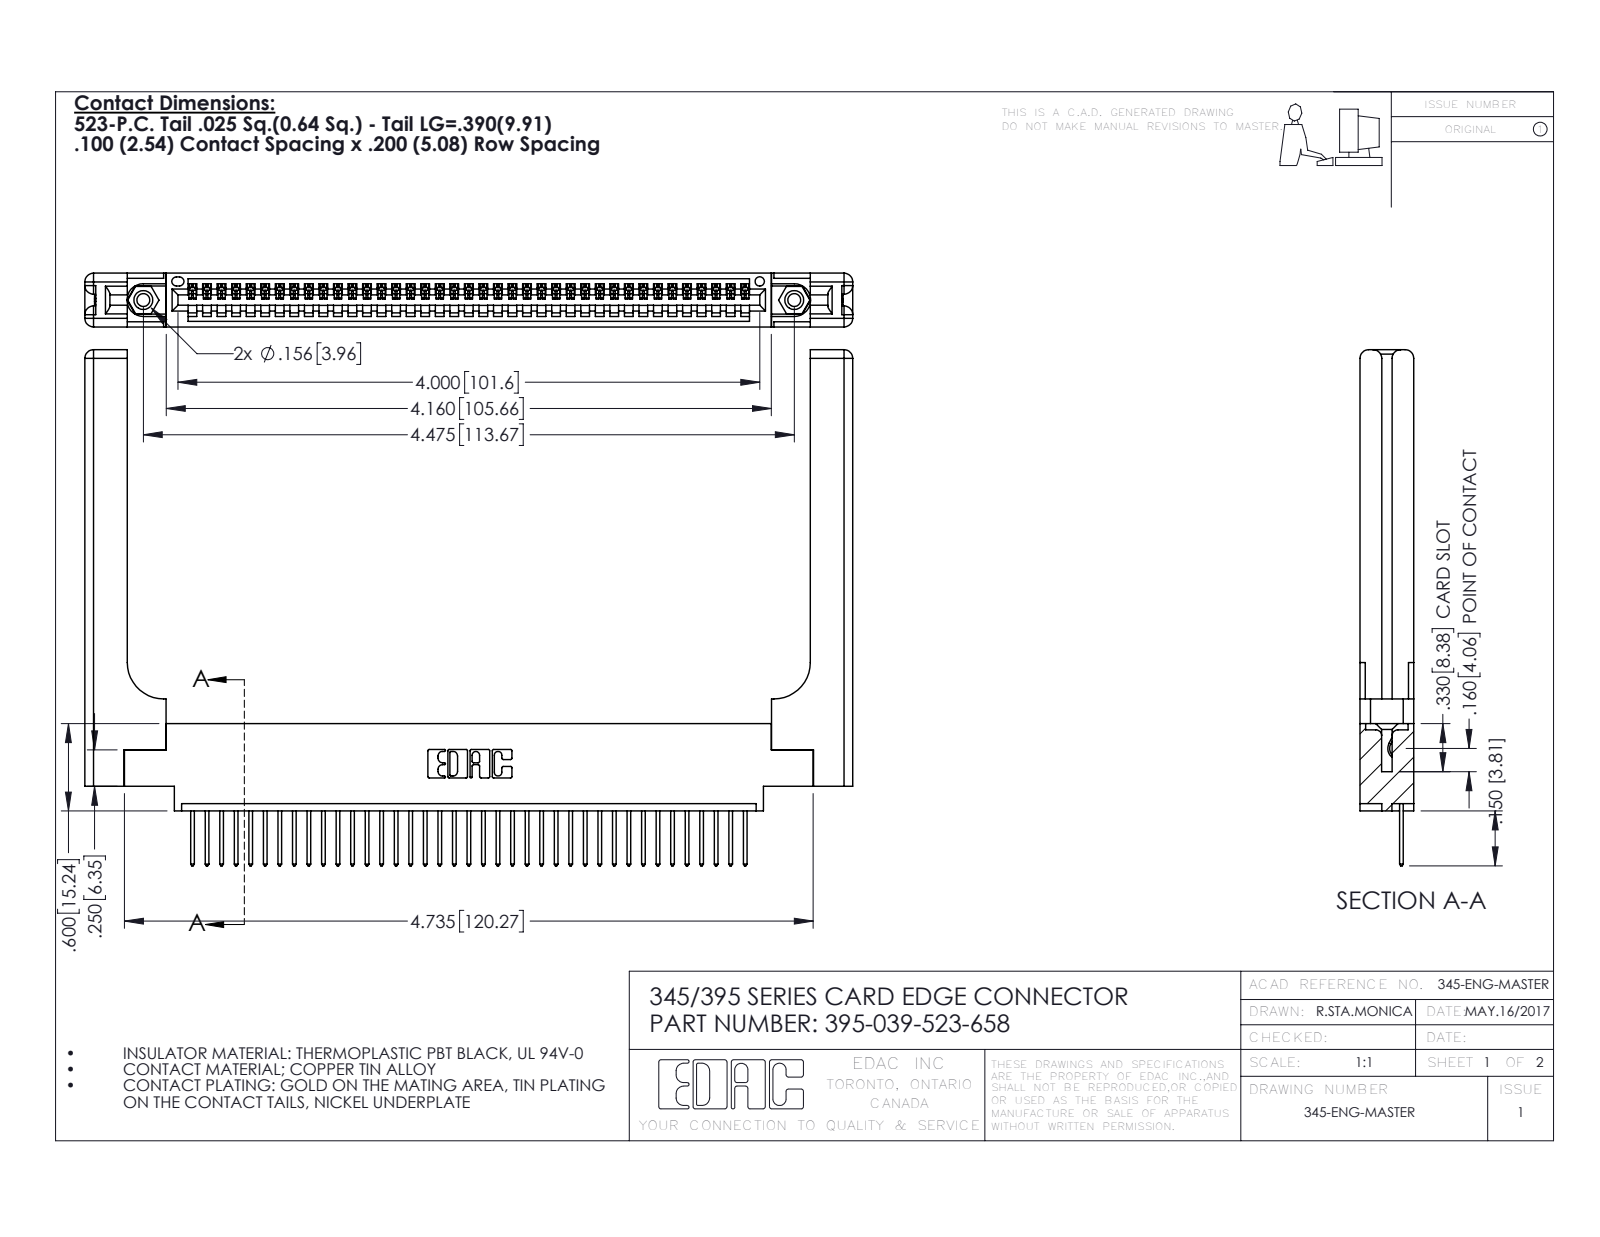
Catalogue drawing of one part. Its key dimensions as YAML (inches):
part_name: "345-250-001_345-250-001-102; 395-039-523-658; 345-292-001_345-293-123; 345 Part_0.170 Offset - 0.156 Dia-TH (+1 more)"
step_written_by: "SolidWorks 2016 (CONFIG_CONTROL_DESIGN)"
units: inches
bodies: {solids: 44, faces: 2648, planar: 1792, cylindrical: 796, other: 60}
overall_size: [5.279, 3.547, 0.37]
volume: 1.287
surface_area: 34.34
round_holes:
  - {diameter: 0.089, count: 2}
  - {diameter: 0.125, count: 2}
  - {diameter: 0.156, count: 2}
  - {diameter: 0.064, count: 1}
round_bosses_or_shafts:
  - {diameter: 0.155, count: 2}
partial_cylinders:
  - {radius: 0.006, count: 78}
  - {radius: 0.01, count: 78}
  - {radius: 0.01, count: 22}
  - {radius: 0.06, count: 16}
  - {radius: 0.007, count: 6}
  - {radius: 0.031, count: 6}
  - {radius: 0.026, count: 3}
  - {radius: 0.03, count: 2}
face_to_face_distances: [0.37, 0.072, 0.298, 0.098, 0.272, 0.025, 0.2, 0.148, 0.15, 0.225]
hole_center_spacings: [0.27, 4.239, 4.475]
